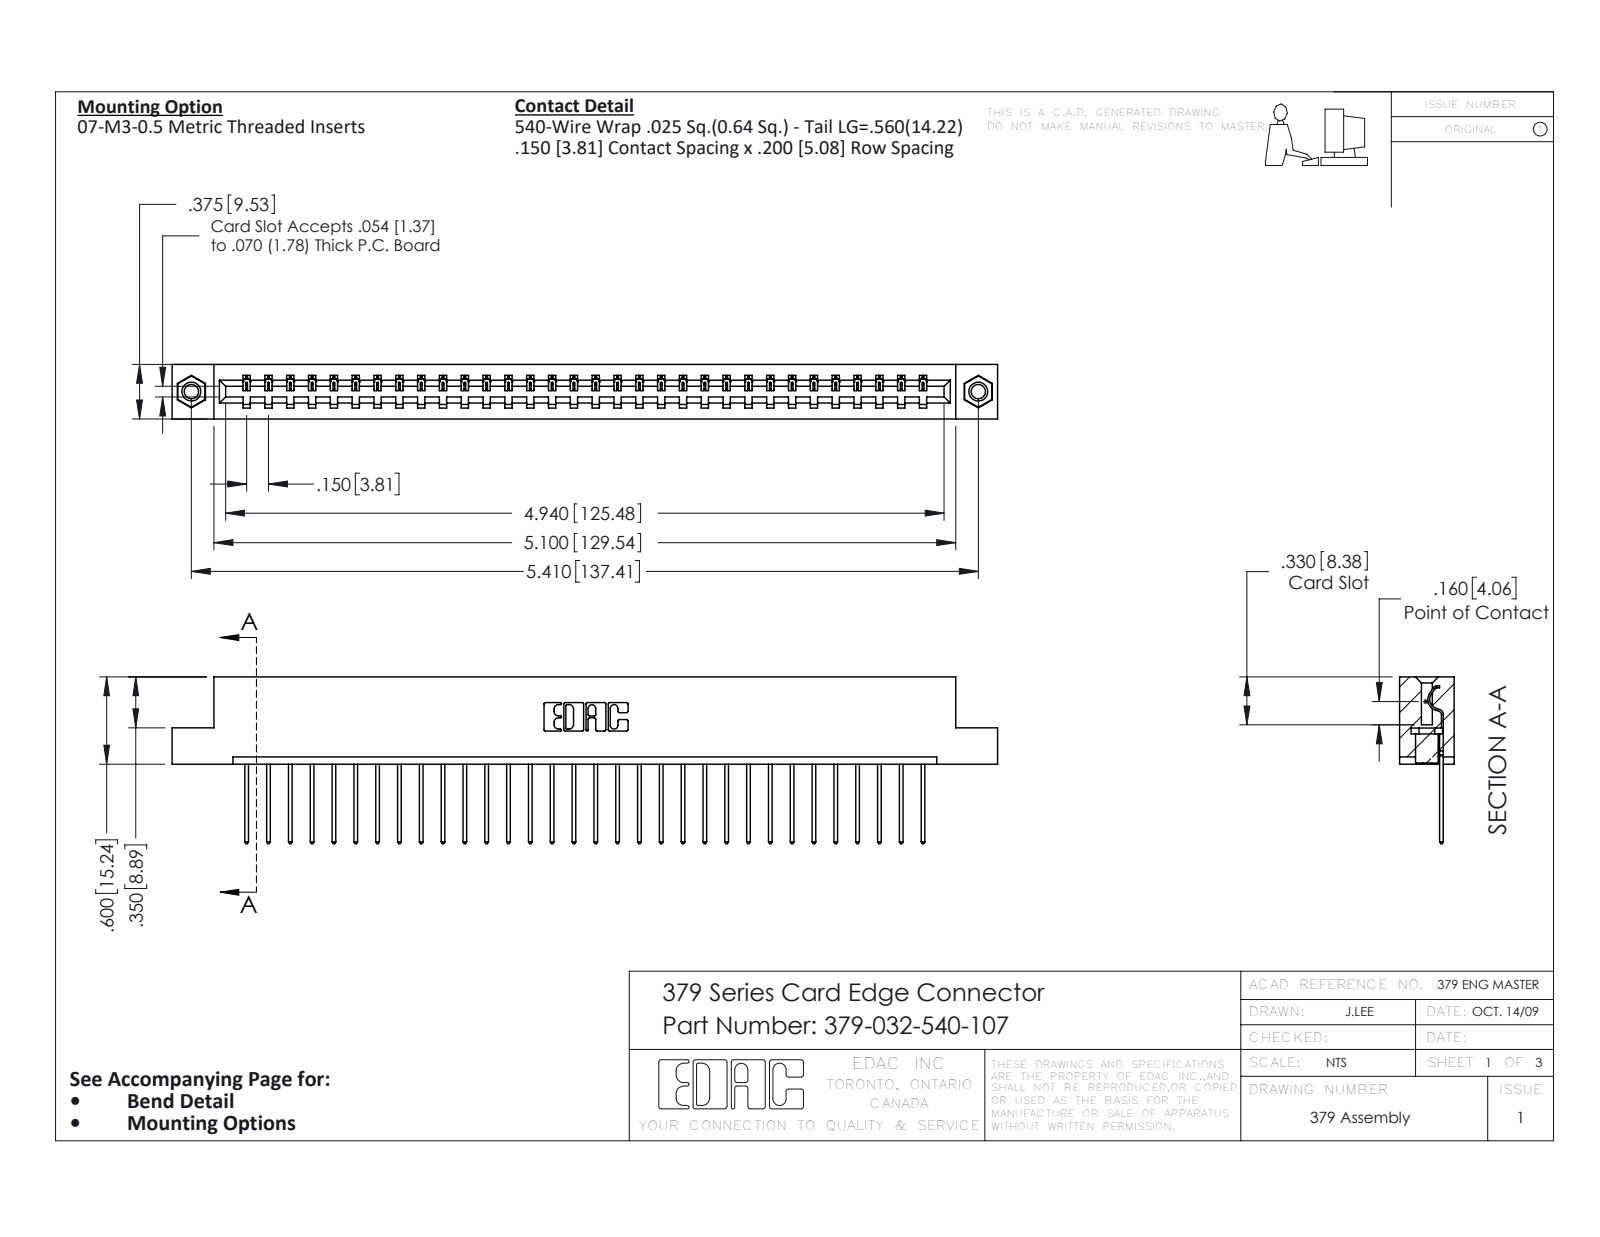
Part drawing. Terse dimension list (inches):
name: 379 Part_Flush - .156 Dia - TI; 379-032-540-107; 345-292-001_345-293-140; 345-250-001_345-250-005-103
written by: SolidWorks 2016 (CONFIG_CONTROL_DESIGN)
unit: in
bodies: 35 solids, 2030 faces (1446 planar, 568 cylindrical, 16 other)
size: 5.675 × 1.147 × 0.375
volume: 0.919 in³; area: 24.36 in²
holes: 2× ⌀0.098, 2× ⌀0.125, 2× ⌀0.156
bosses: 2× ⌀0.155
rounds: 64× R0.006, 64× R0.01, 22× R0.01, 6× R0.007, 6× R0.031, 3× R0.026, 1× R0.014, 1× R0.022
face distances: 0.3, 0.075, 0.375, 0.225, 0.275, 0.1, 0.025, 0.2, 0.6, 0.55
hole spacings: 5.41
